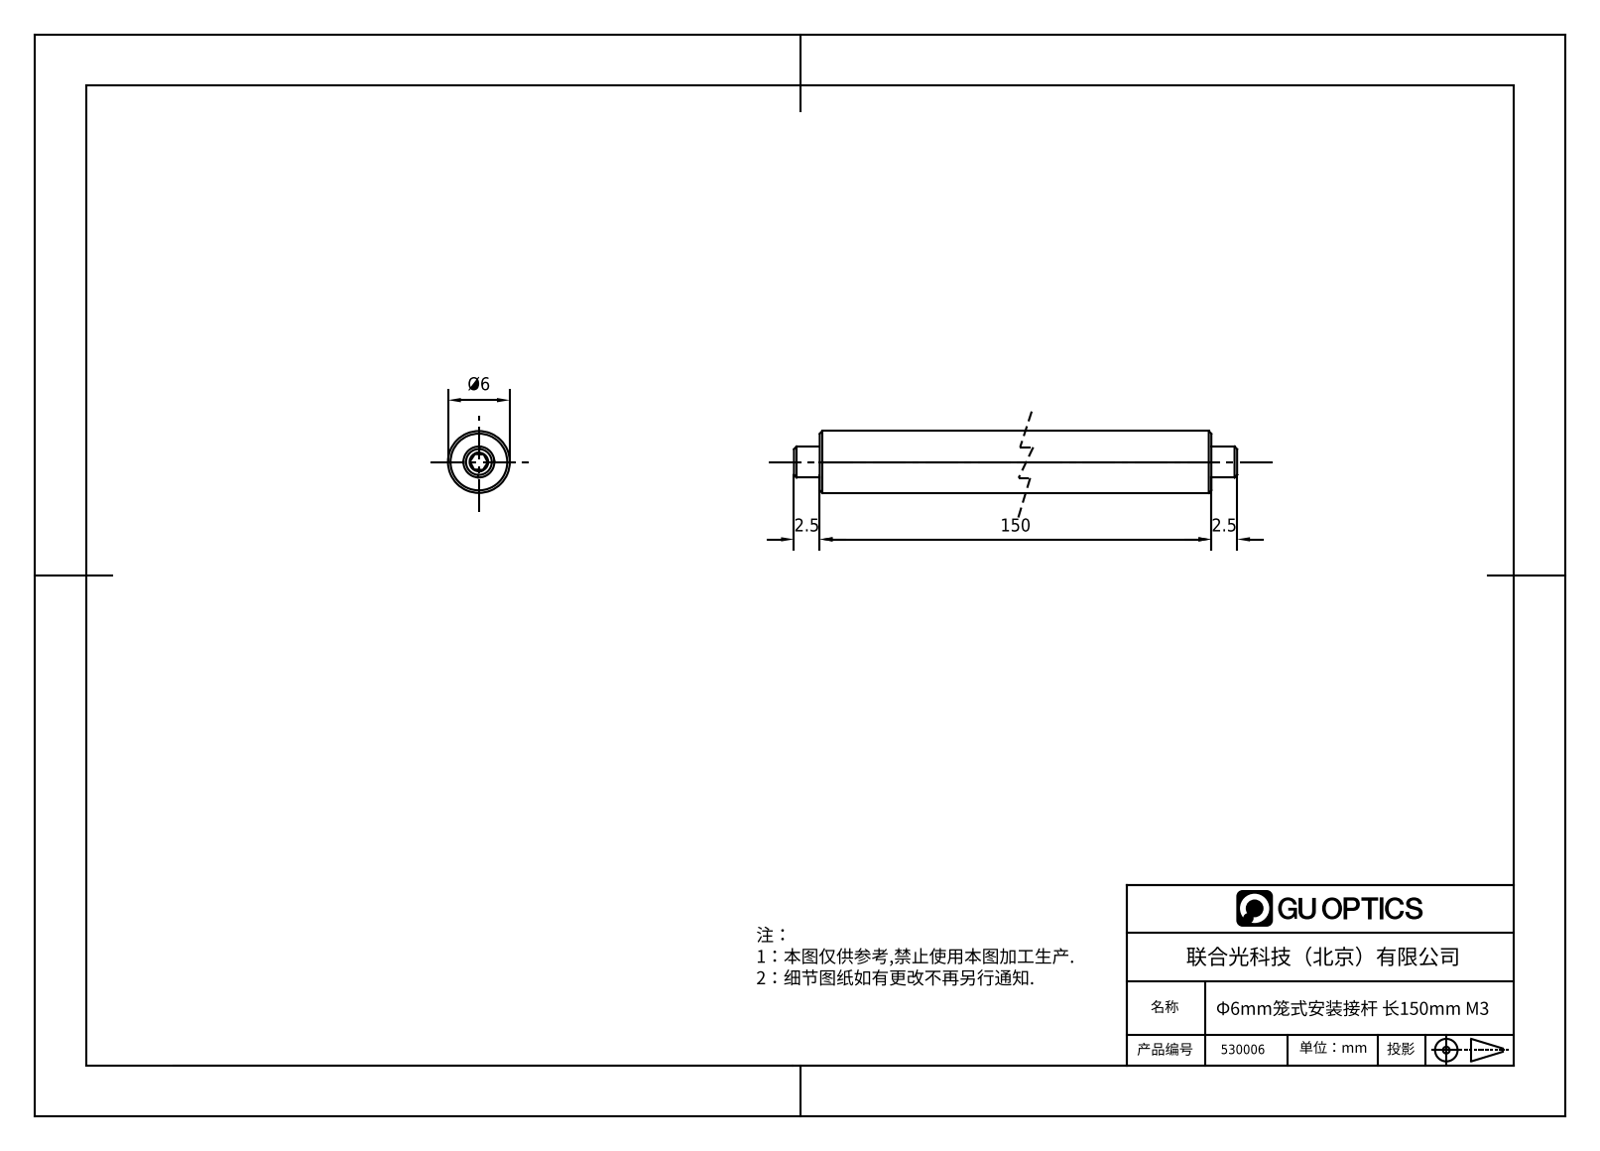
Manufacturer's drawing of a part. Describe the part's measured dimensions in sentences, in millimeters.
Its 3-D file was written by "SolidWorks 2018 (AUTOMOTIVE_DESIGN)". It is 0 solids with 36 faces: 18 planar, 6 cylindrical and 12 other. Overall it measures 155 by 6 by 6 millimeters. Round bosses or shafts: 1 of diameter 6, 1 of diameter 3. The main face-to-face distances are 150, 1.5, 2.5, 152.5, 1, 154, 151.5, 155, 153.
